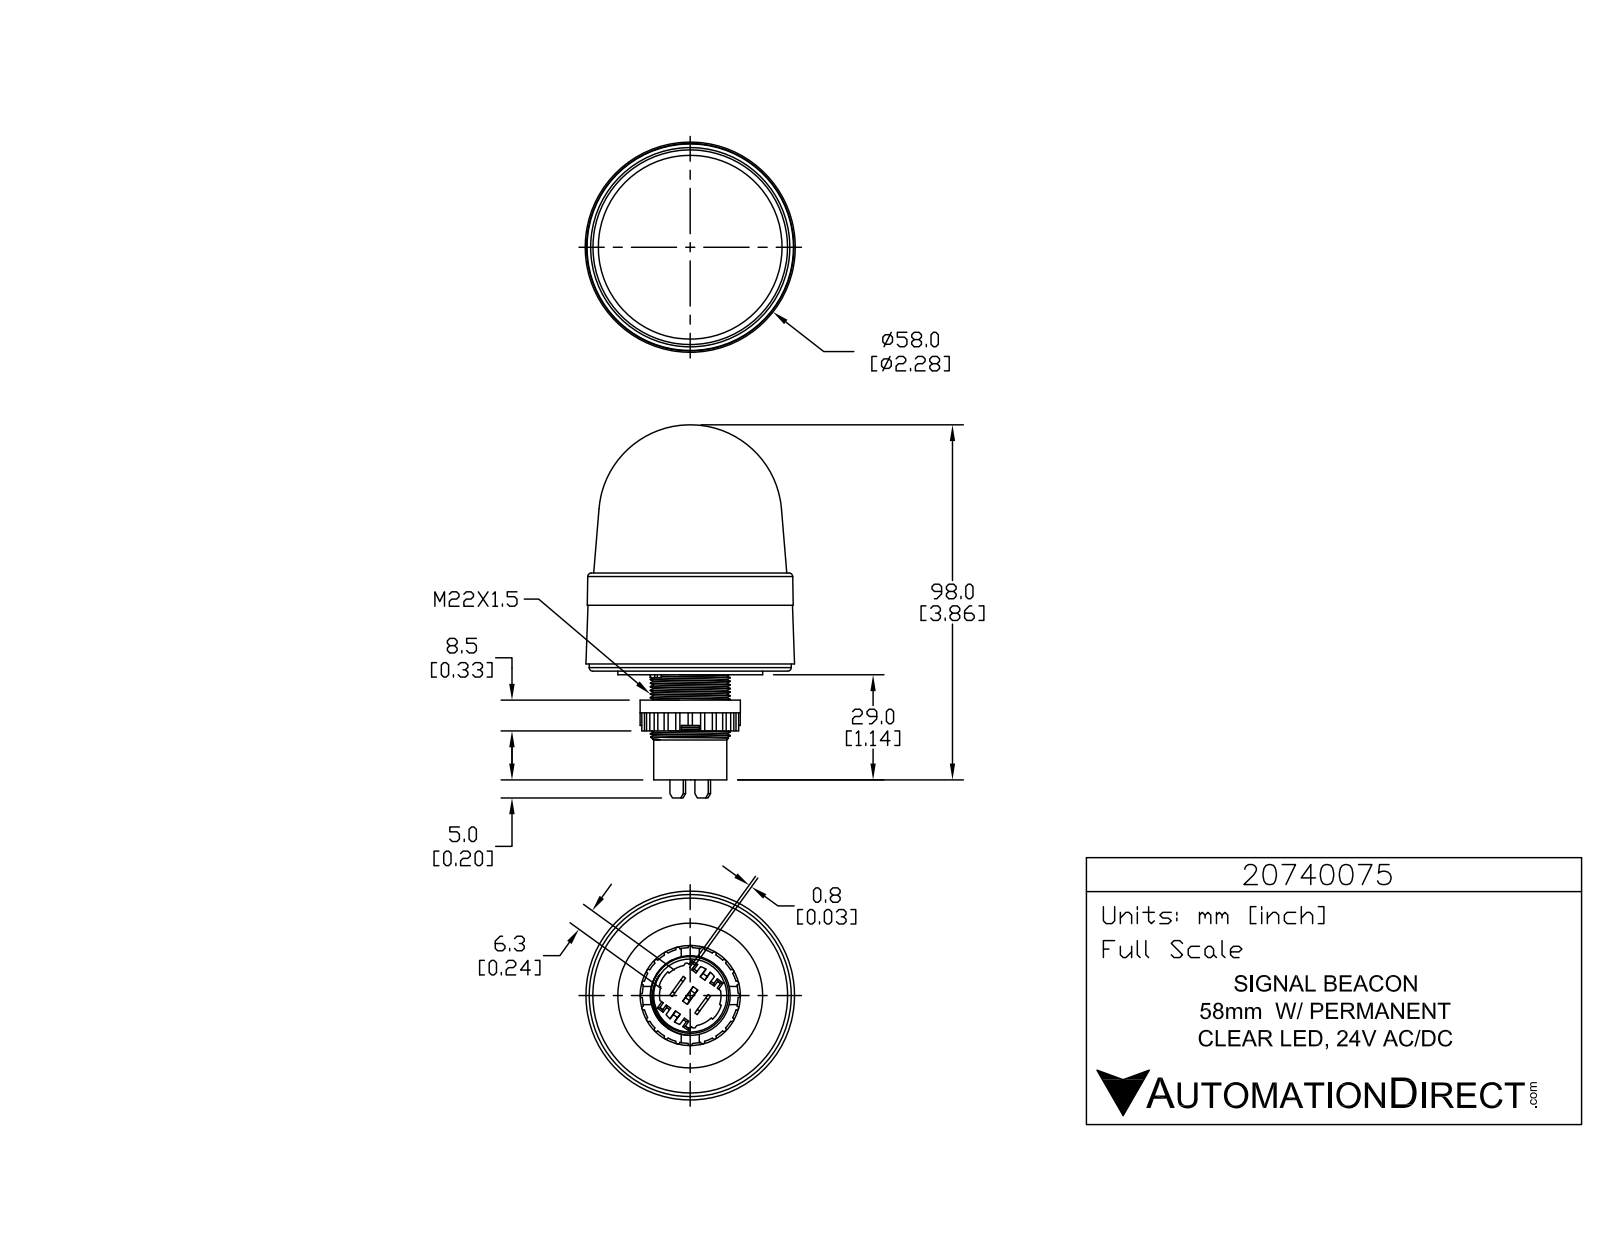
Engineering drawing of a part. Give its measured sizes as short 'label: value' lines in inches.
name: 20740075
written by: SolidWorks 2015 (AUTOMOTIVE_DESIGN)
unit: in
bodies: 1 solid, 266 faces (119 planar, 120 cylindrical, 27 other)
size: 4.051 × 2.269 × 2.269
volume: 9.016 in³; area: 31.05 in²
holes: 1× ⌀0.906
bosses: 1× ⌀2.197, 1× ⌀1.575, 1× ⌀1.091, 1× ⌀0.866, 1× ⌀0.795
rounds: 24× R0.023, 2× R0.02, 1× R0.335, 1× R0.354, 1× R0.522
face distances: 0.039, 0.276, 0.118, 1.142, 0.335, 0.315, 1.063, 0.748, 1.024, 0.728
